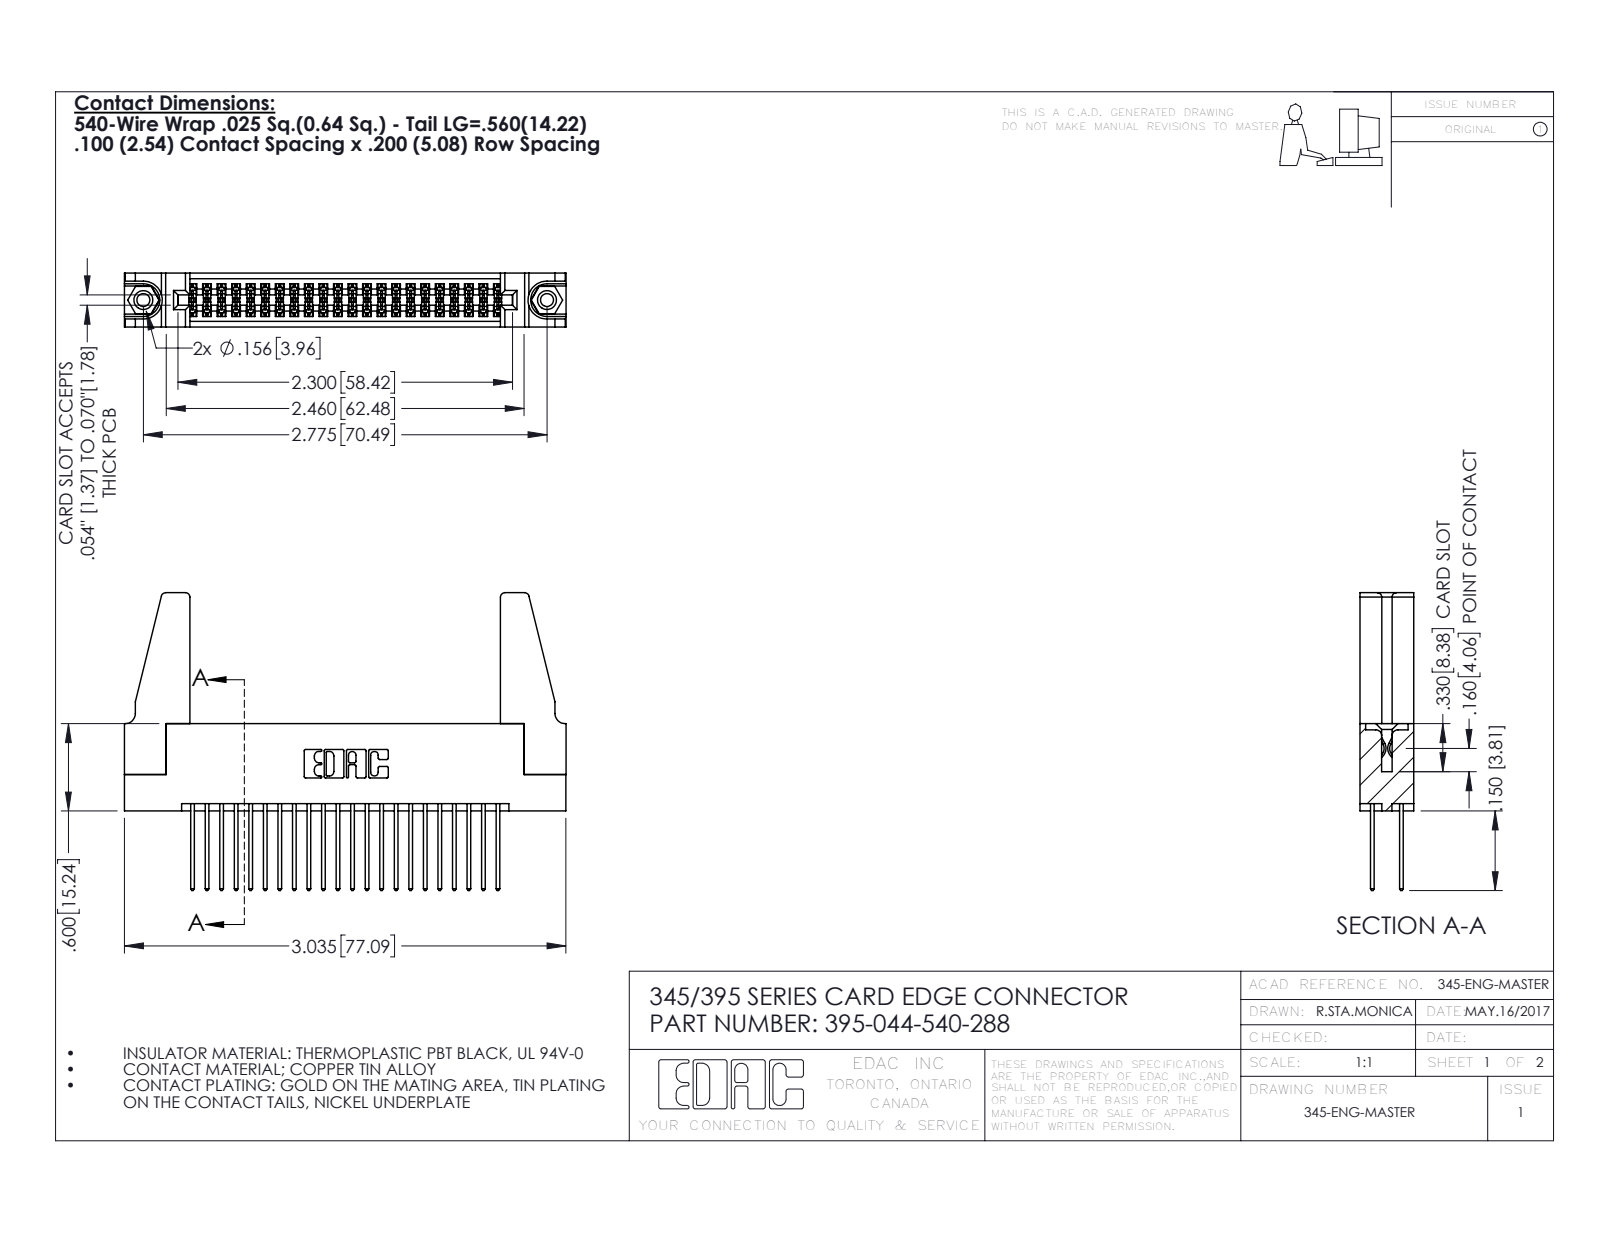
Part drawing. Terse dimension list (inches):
name: 395-044-540-288; 345-220-078_345-220-088; 345-292-001_345-293-140; 345 Part_Flush Mounting Lugs - 0.156 Dia-TH (+1 more)
written by: SolidWorks 2016 (CONFIG_CONTROL_DESIGN)
unit: in
bodies: 49 solids, 2450 faces (1604 planar, 830 cylindrical, 16 other)
size: 3.036 × 2.047 × 0.37
volume: 0.654 in³; area: 22.56 in²
holes: 2× ⌀0.089, 2× ⌀0.125, 2× ⌀0.156, 1× ⌀0.064
bosses: 2× ⌀0.155
rounds: 66× R0.006, 44× R0.01, 22× R0.01, 8× R0.03, 6× R0.007, 6× R0.031, 3× R0.026, 2× R0.014
face distances: 0.072, 0.298, 0.2, 0.37, 0.098, 0.272, 0.025, 0.225, 0.175, 0.149
hole spacings: 0.27, 2.541, 2.775
